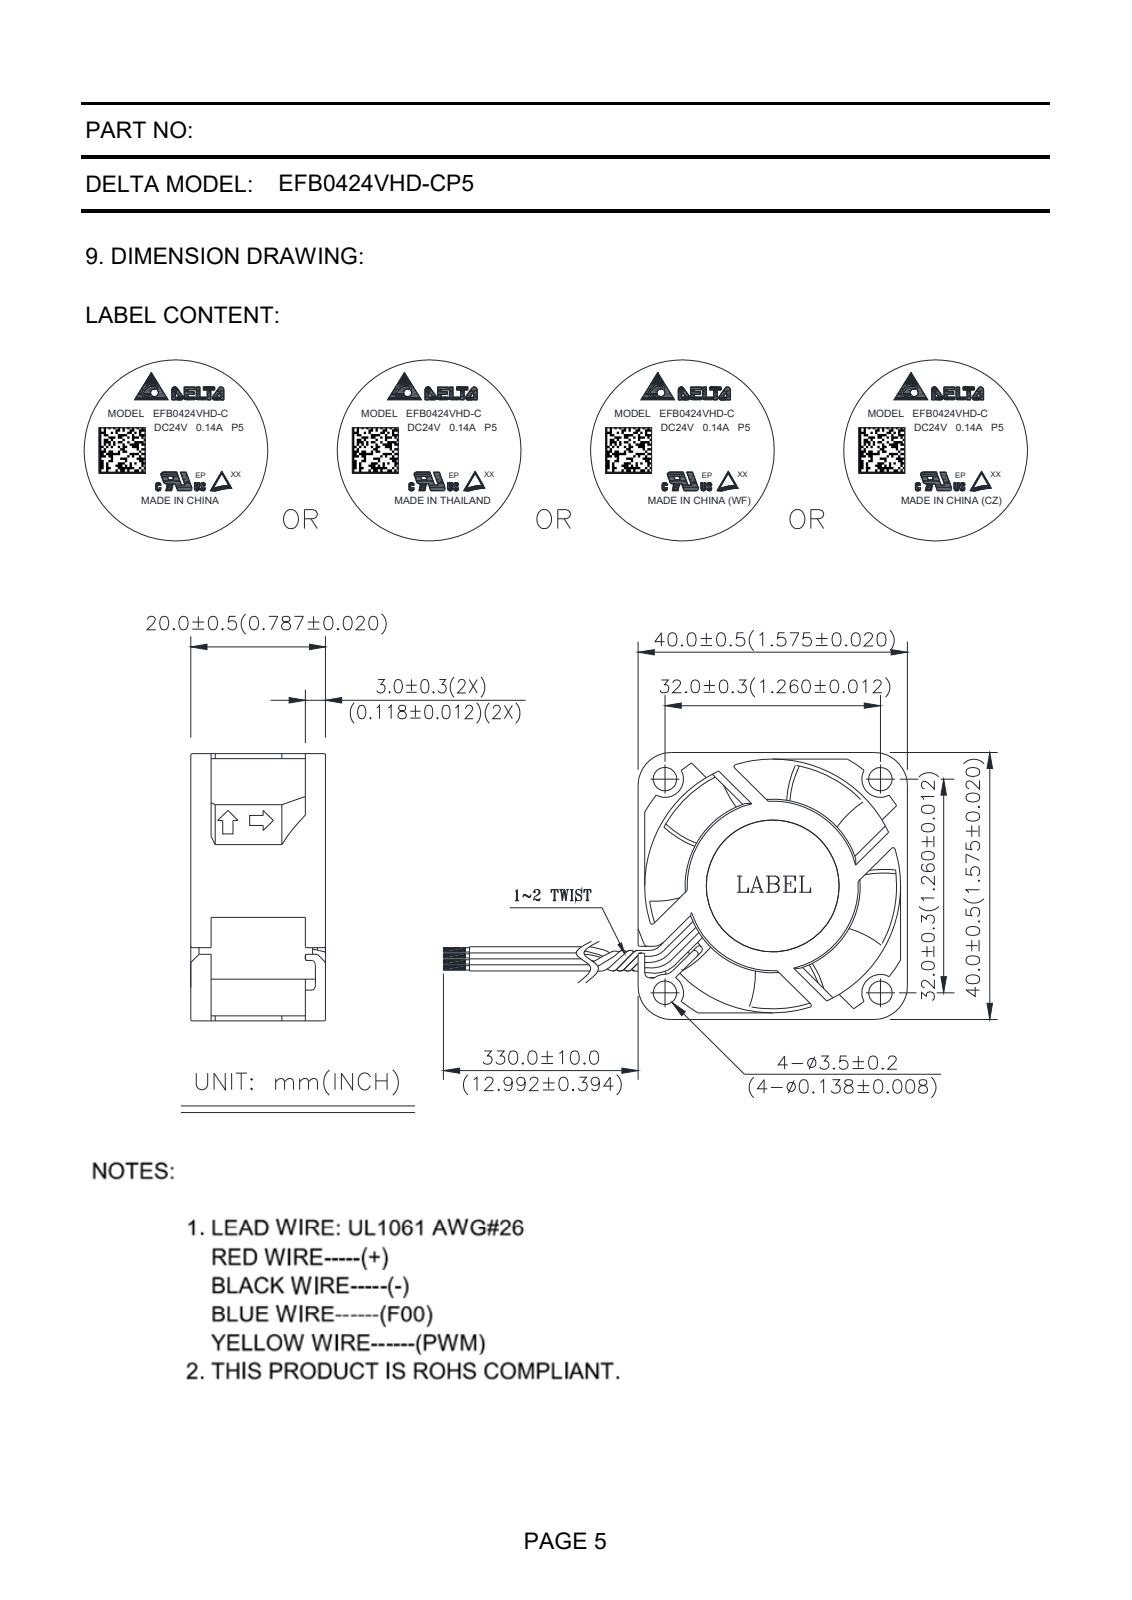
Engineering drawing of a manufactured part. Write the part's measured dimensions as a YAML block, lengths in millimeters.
part_name: "PRT0020_1_1; PRT0021_1_1; ASM0008_ASM_1_1_ASM; EFB4020_ASM_ASM"
step_written_by: "CREO PARAMETRIC BY PTC INC, 2020454 (AUTOMOTIVE_DESIGN)"
units: millimeters
bodies: {solids: 2, faces: 149, planar: 63, cylindrical: 43, other: 43}
overall_size: [46.31, 45.86, 21.05]
volume: 17354
surface_area: 12043
round_holes:
  - {diameter: 3.5, count: 4}
  - {diameter: 38, count: 1}
round_bosses_or_shafts:
  - {diameter: 26.12, count: 1}
  - {diameter: 26, count: 1}
partial_cylinders:
  - {radius: 3.25, count: 4}
  - {radius: 5, count: 4}
  - {radius: 0.3, count: 1}
  - {radius: 0.4, count: 1}
  - {radius: 0.5, count: 1}
  - {radius: 0.7, count: 1}
  - {radius: 2, count: 1}
  - {radius: 2.75, count: 1}
face_to_face_distances: [1, 6, 5, 20.01, 15.01, 14.01, 40, 20.07, 15.07, 14.07]
hole_center_spacings: [32, 22.63, 45.26, 22.62]
